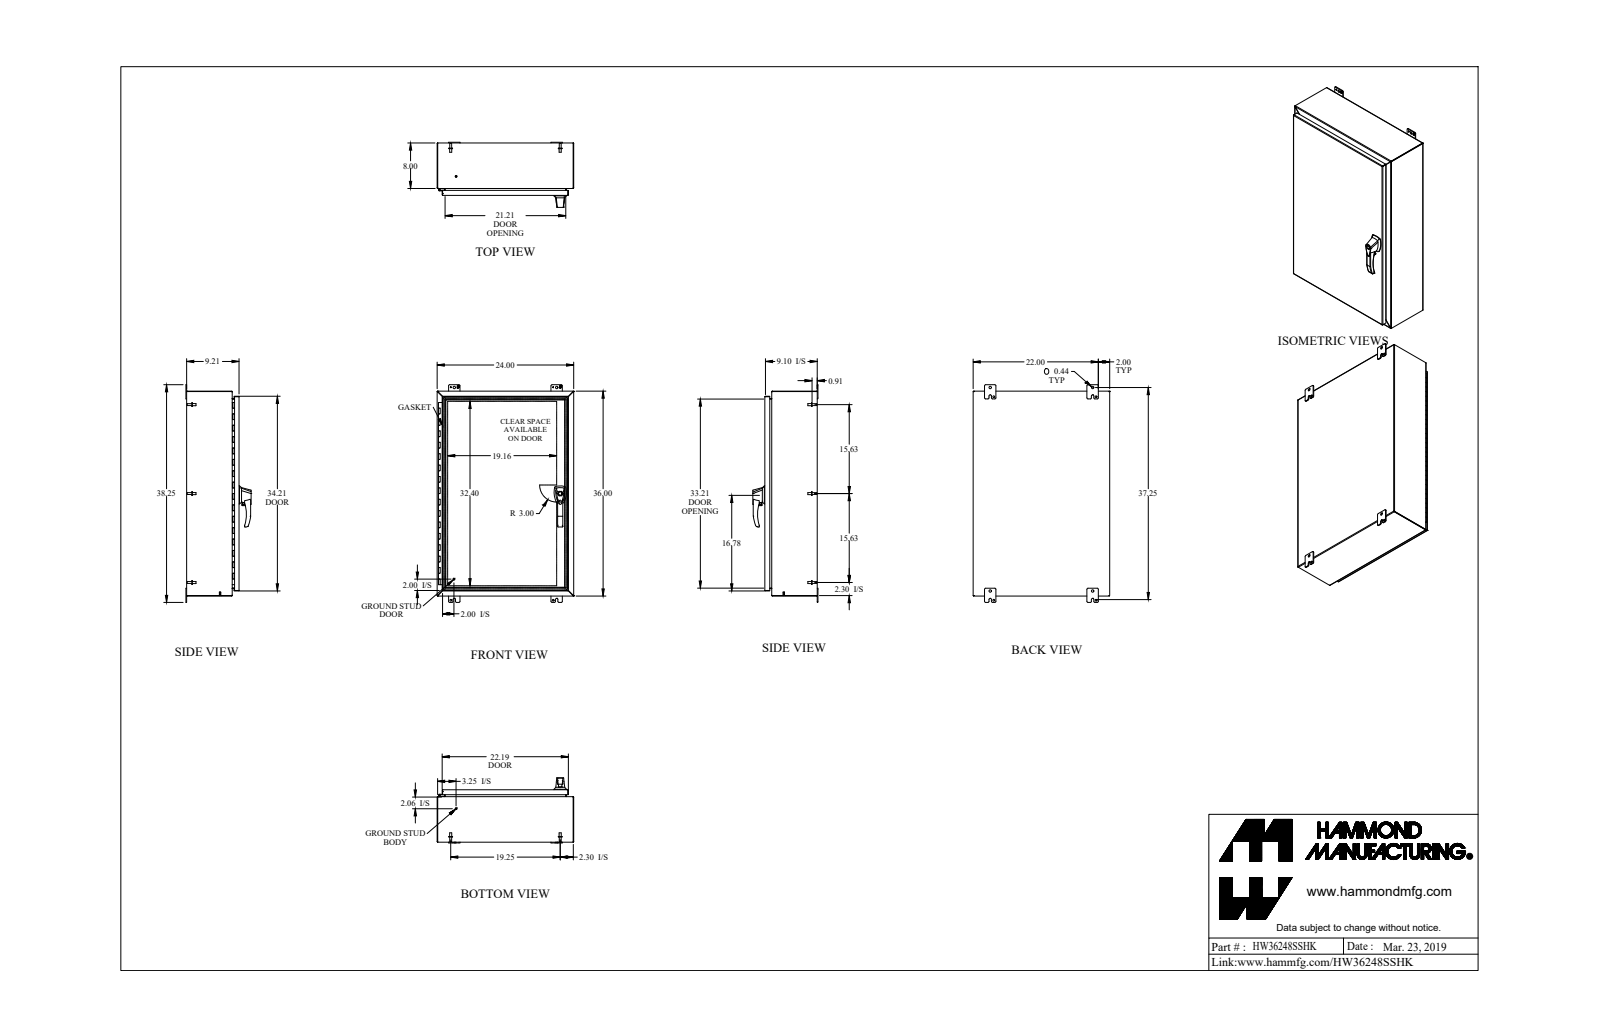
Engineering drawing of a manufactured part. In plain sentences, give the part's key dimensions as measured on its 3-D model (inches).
The part is named "HW36248SSHK". Its 3-D file was written by "SolidWorks 2018 (AUTOMOTIVE_DESIGN)". It is 44 solids with 1544 faces: 737 planar, 641 cylindrical and 166 other. Overall it measures 38.25 by 24 by 11.45 inches. Its volume is 252.9 cubic inches and its surface area 6 594 square inches. Round holes: 6 of diameter 0.176, 5 of diameter 0.313, 3 of diameter 0.25, 3 of diameter 0.265, 3 of diameter 0.413, 2 of diameter 0.196, 2 of diameter 0.256, 2 of diameter 0.394, 2 of diameter 0.437, 1 of diameter 0.187, 1 of diameter 0.233, 1 of diameter 0.33. Round bosses or shafts: 11 of diameter 0.375, 7 of diameter 0.25, 6 of diameter 0.65, 6 of diameter 0.332, 6 of diameter 0.156, 3 of diameter 1, 3 of diameter 0.51, 2 of diameter 0.63. Partial cylindrical surfaces (rounded edges, fillets, slot ends): 27 of radius 0.25, 24 of radius 0.188, 20 of radius 0.036, 20 of radius 0.108, 12 of radius 0.06, 9 of radius 0.125, 8 of radius 0.045, 8 of radius 0.218. The main face-to-face distances are 0.072, 9.138, 9.066, 0.072, 9.138, 9.21, 23.928, 35.928, 7.928, 23.856. The hole center spacings are 1.11, 14.118, 14.119, 28.237, 14.119, 18, 37.38, 1.004.
